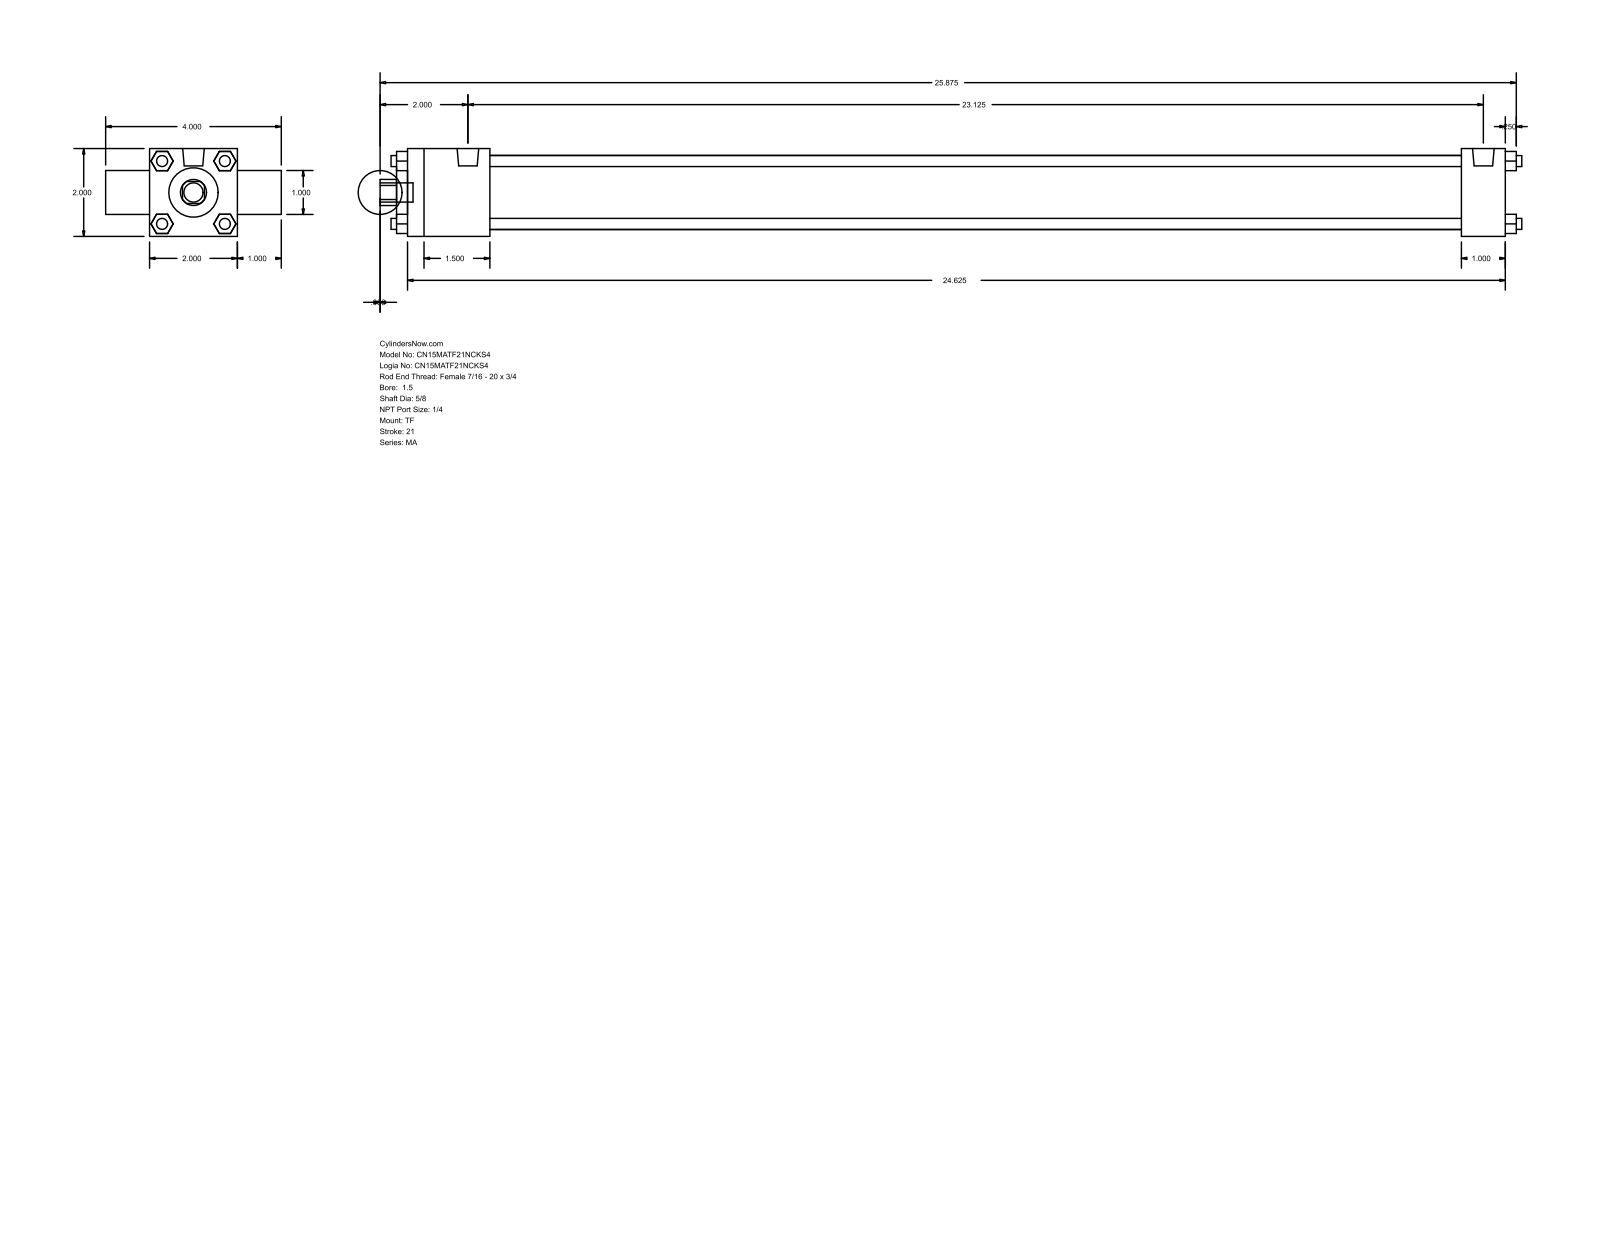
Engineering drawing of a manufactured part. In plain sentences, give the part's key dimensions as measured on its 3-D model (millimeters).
The part is named "MA_TF__0150_0.625". Its 3-D file was written by "GSSL Pune (CONFIG_CONTROL_DESIGN)". It is 0 solids with 120 faces: 92 planar, 28 cylindrical and 0 other. Overall it measures 660.4 by 101.6 by 50.8 millimeters. Round holes: 1 of diameter 15.88, 1 of diameter 25.4, 1 of diameter 28.57, 1 of diameter 42.93. Round bosses or shafts: 4 of diameter 6.35, 3 of diameter 7.94, 2 of diameter 12.49, 1 of diameter 11.11. Partial cylindrical surfaces (rounded edges, fillets, slot ends): 1 of radius 7.54. The main face-to-face distances are 50.8, 25.4, 635, 641.35, 6.35, 76.2, 47.62, 609.6, 561.98, 587.38.
